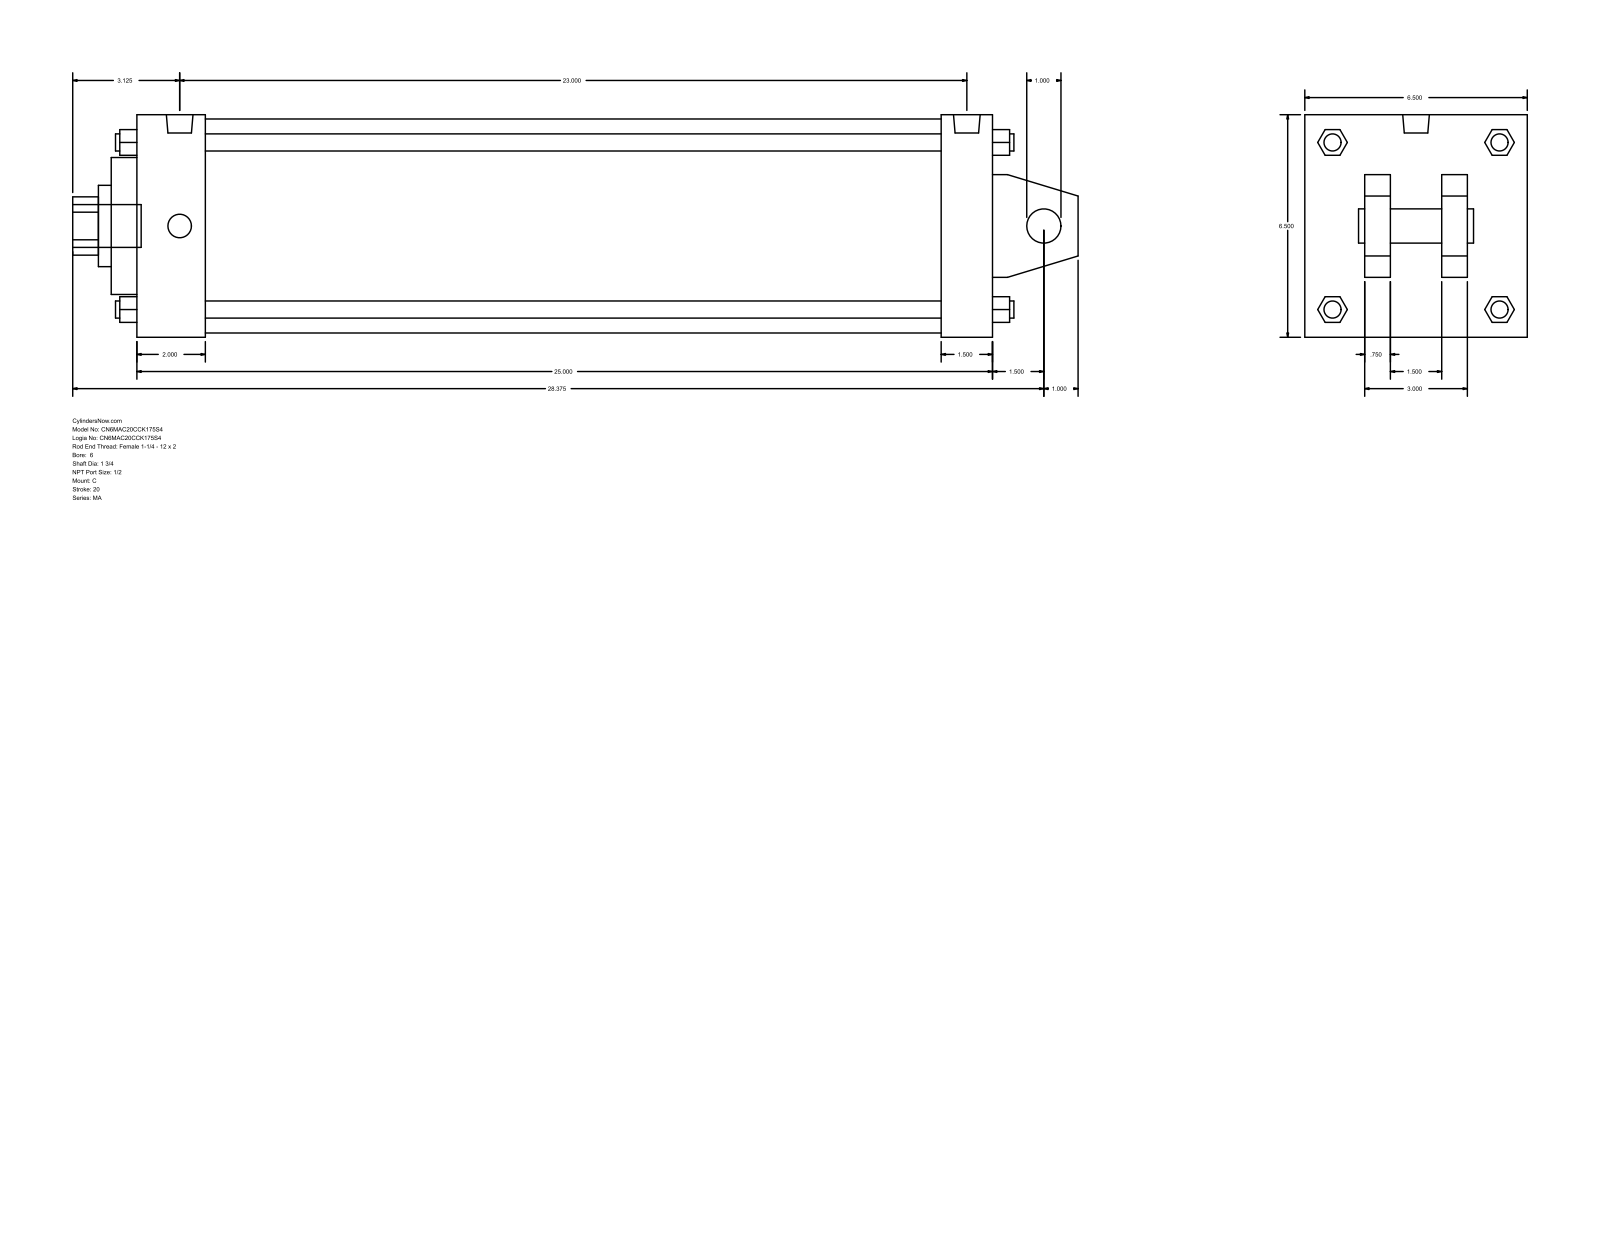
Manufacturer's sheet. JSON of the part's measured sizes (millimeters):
{"part_name": "MA_C__0600_1.75", "step_written_by": "GSSL Pune (CONFIG_CONTROL_DESIGN)", "units": "millimeters", "bodies": {"solids": 0, "faces": 141, "planar": 109, "cylindrical": 32, "other": 0}, "overall_size": [746.12, 165.1, 165.1], "round_holes": [[25.4, 1], [44.45, 1], [60.33, 1], [101.6, 1], [158.75, 1]], "round_bosses_or_shafts": [[17.46, 4], [12.7, 4], [19.77, 2], [31.75, 1]], "partial_cylinders_radius": [[21.63, 1]], "face_to_face_distances": [165.1, 635, 19.05, 38.1, 63.5, 101.6, 44.45, 120.65, 57.15, 50.8]}
